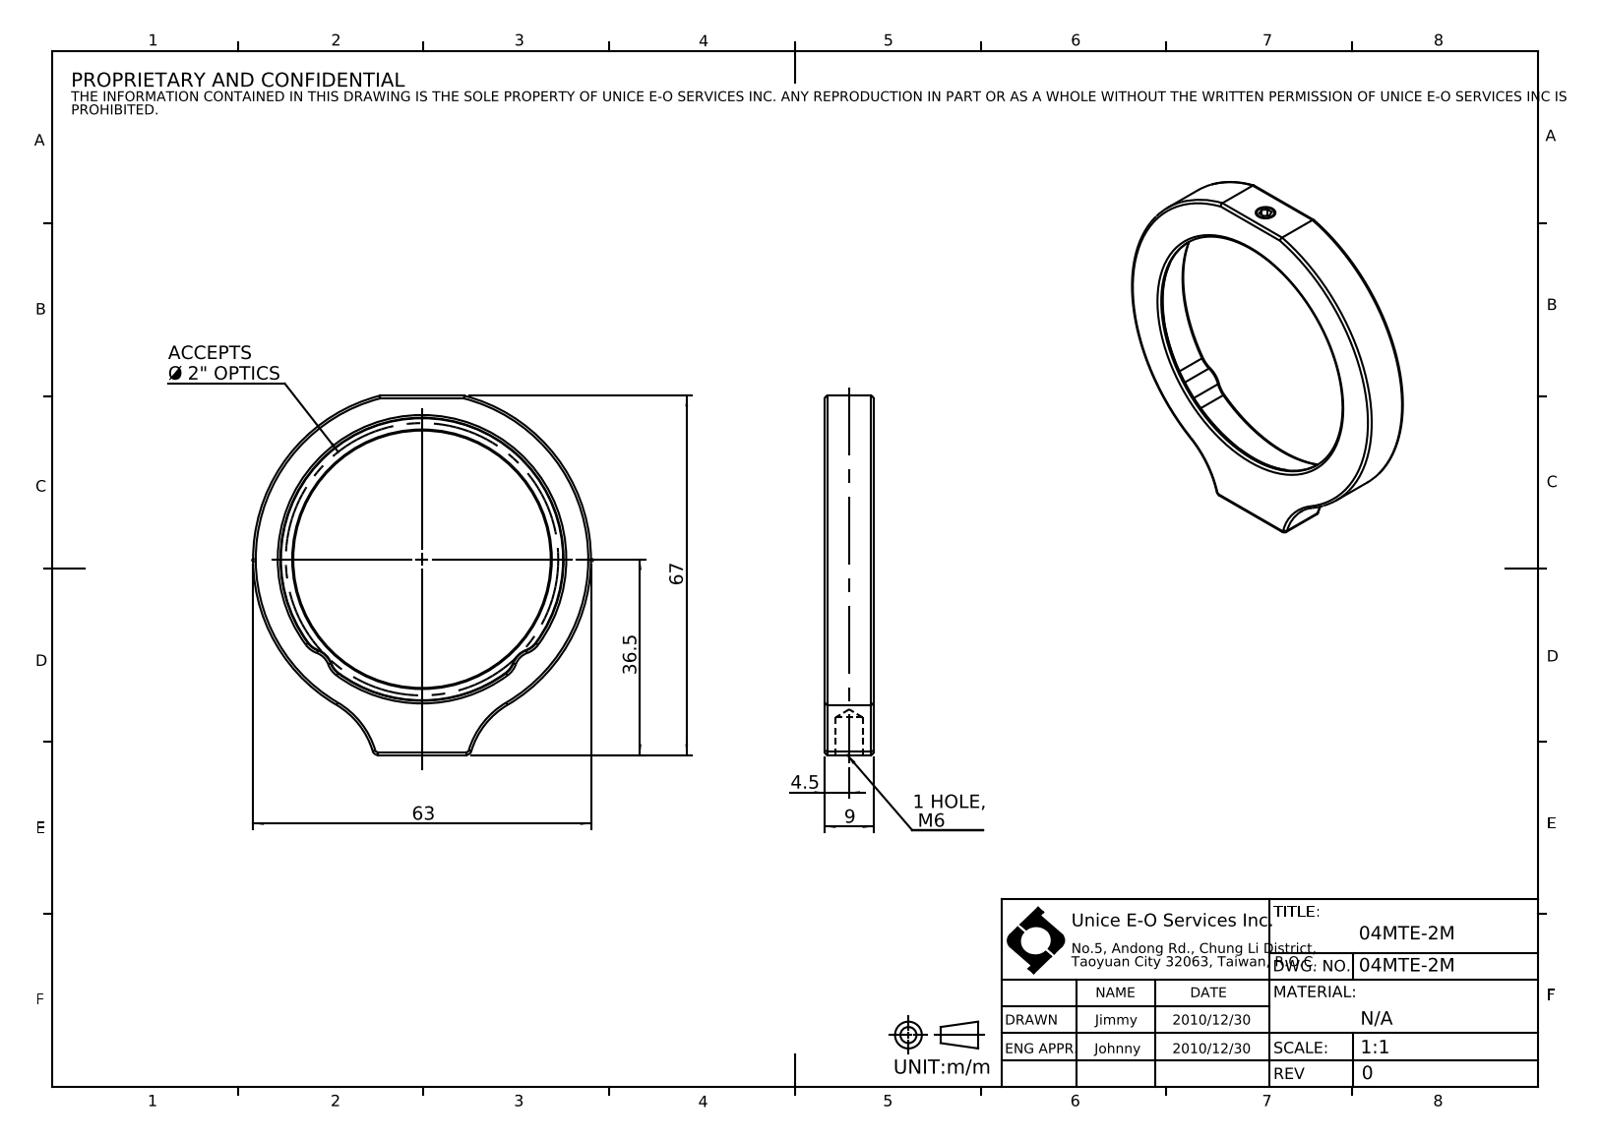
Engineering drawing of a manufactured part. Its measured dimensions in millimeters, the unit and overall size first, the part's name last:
Units: millimetres
Overall size (bounding box): 67 × 63 × 9
Round holes (diameter × count): ⌀1.5 ×1, ⌀3.3 ×1, ⌀5 ×1, ⌀48 ×1, ⌀52.8 ×1
Round bosses / shafts (diameter × count): ⌀4 ×1, ⌀1.6 ×1
Partial cylindrical surfaces — rounded edges, fillets, slot ends (radius × count): R4 ×6, R0.5 ×4, R1 ×2, R15 ×2, R31.5 ×1
Main face-to-face distances: 9, 1, 8, 67, 2, 63, 4, 2.5, 64.5, 1.5
Hole centre spacings: 0.5
Volume: 9 604 mm³ · Surface area: 6 239 mm²
Bodies: 3 solids, 95 faces (16 planar, 33 cylindrical, 46 other)
Part name (STEP PRODUCT): 04MTE-2M
STEP written by: SolidWorks 2016 (CONFIG_CONTROL_DESIGN)
